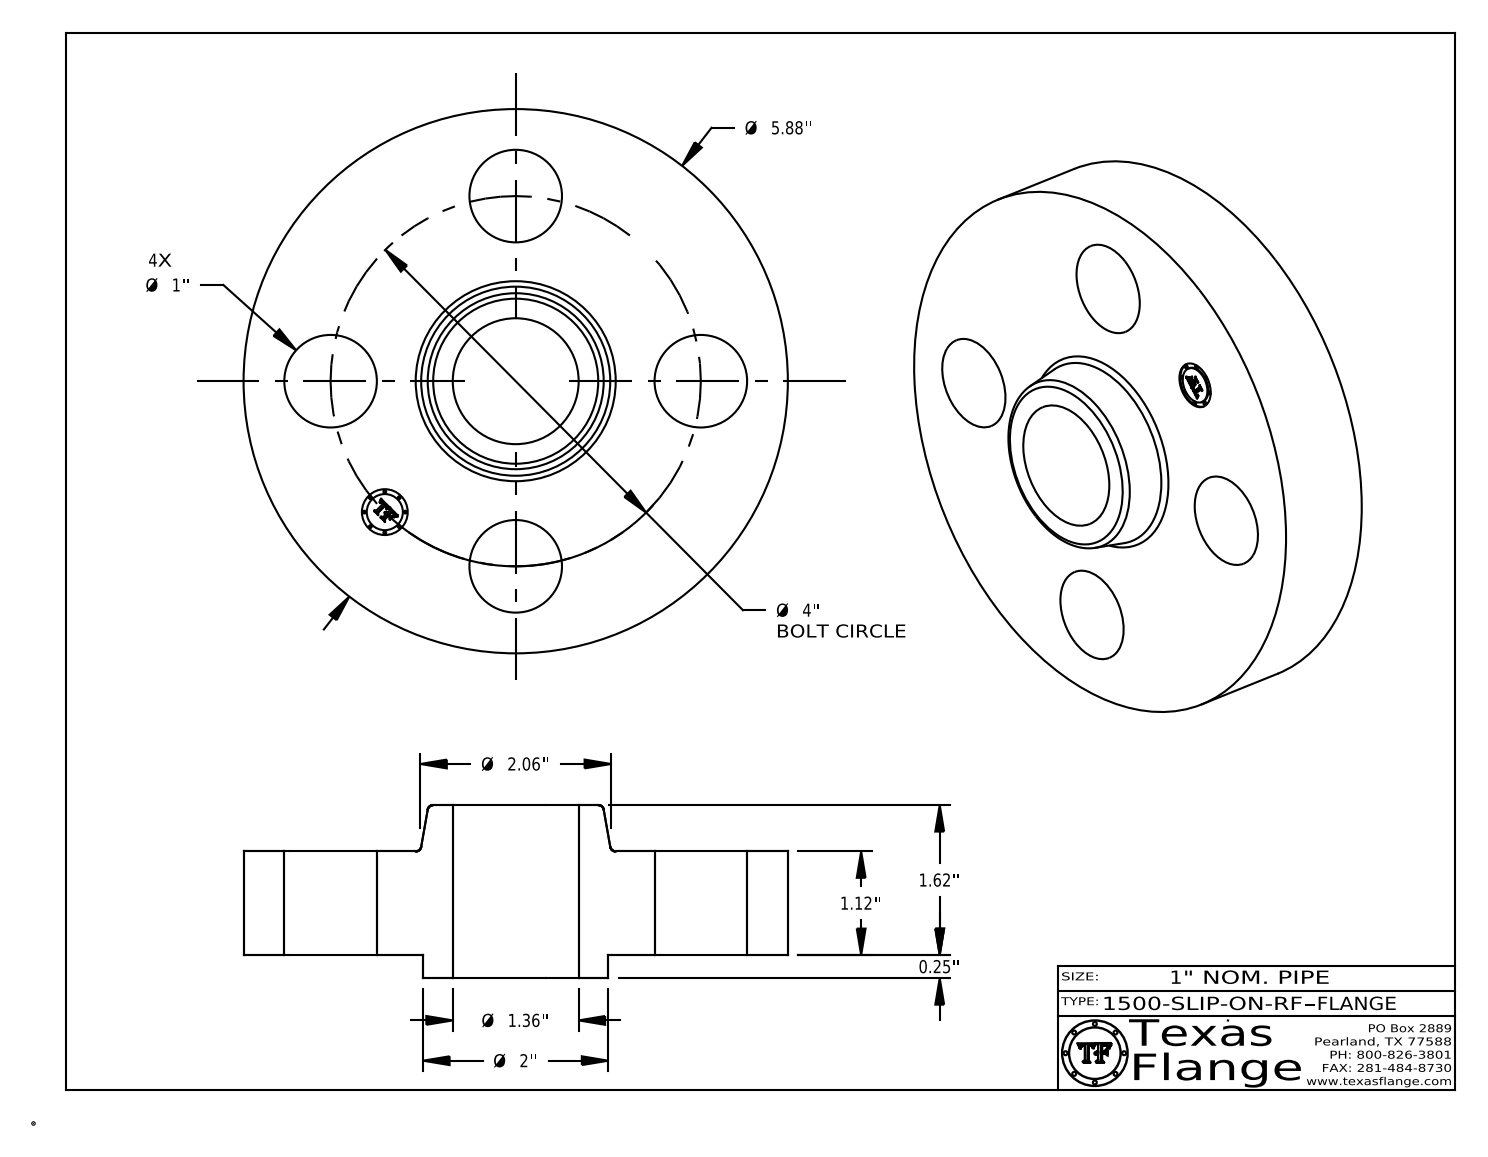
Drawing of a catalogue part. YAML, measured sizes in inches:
part_name: "1500-SLIP-ON-RF"
step_written_by: "CATIA V5 STEP AP214 (AUTOMOTIVE_DESIGN)"
units: inches
bodies: {solids: 1, faces: 409, planar: 369, cylindrical: 34, other: 6}
overall_size: [5.88, 5.88, 1.87]
volume: 26.49
surface_area: 91.93
round_holes:
  - {diameter: 1, count: 4}
  - {diameter: 0.495, count: 1}
  - {diameter: 1.36, count: 1}
round_bosses_or_shafts:
  - {diameter: 0.03, count: 8}
  - {diameter: 5.88, count: 1}
  - {diameter: 2, count: 1}
  - {diameter: 0.39, count: 1}
face_to_face_distances: [1.12, 0.25, 1.37, 1.87, 1.62, 0.5, 0.015, 1.355, 1.105, 0.515]
hole_center_spacings: [2, 2.828, 1.531, 3.695, 4]
